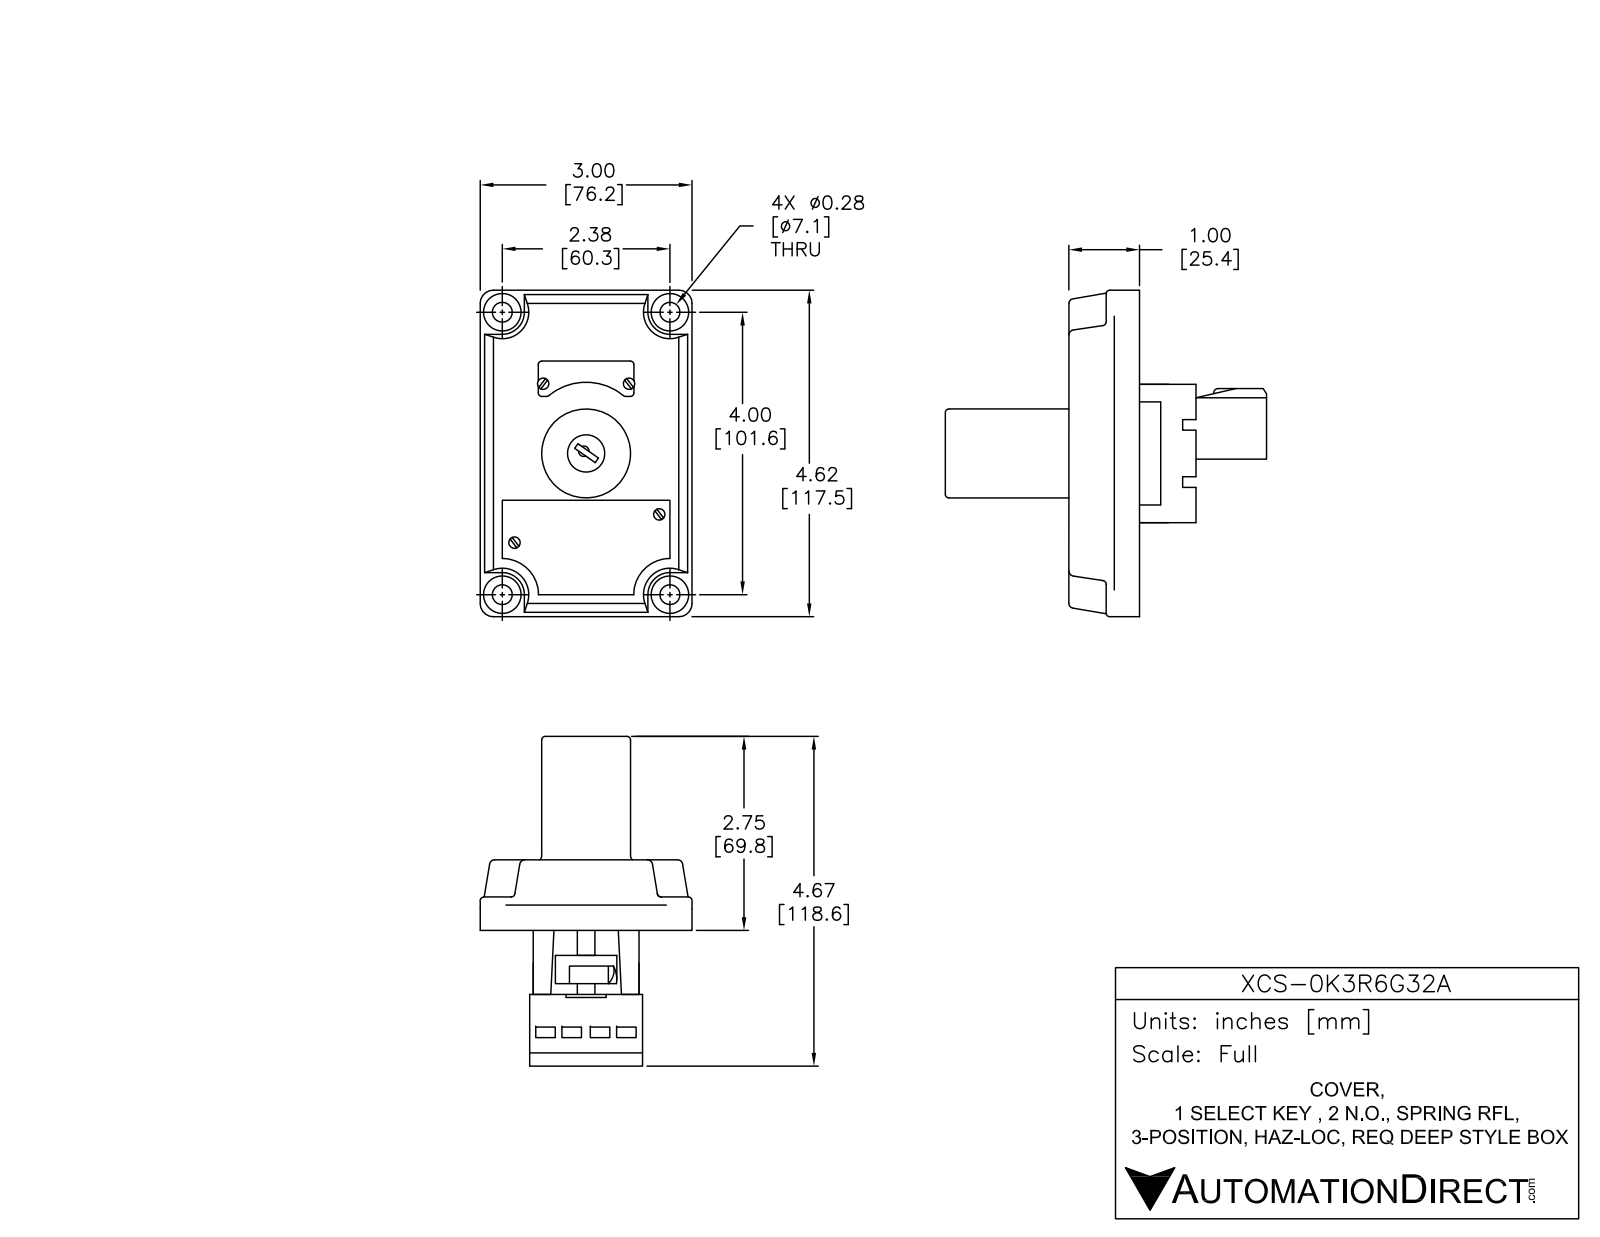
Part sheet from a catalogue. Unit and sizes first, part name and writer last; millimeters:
Units: millimetres
Overall size (bounding box): 117.6 × 106.46 × 78.74
Round holes (diameter × count): ⌀6.65 ×4, ⌀6.86 ×4, ⌀13.41 ×1
Round bosses / shafts (diameter × count): ⌀3.3 ×6, ⌀11.6 ×4, ⌀6.35 ×4, ⌀32 ×1
Partial cylindrical surfaces — rounded edges, fillets, slot ends (radius × count): R0.25 ×28, R1.27 ×10, R0.51 ×8, R1.4 ×8, R3 ×8, R2.38 ×4, R2.54 ×4, R9.65 ×4
Main face-to-face distances: 13.34, 12.7, 26.04, 11.3, 24, 37.34, 17.5, 6.5, 4.8, 30.84
Hole centre spacings: 59.11, 10.2, 20.4, 60.46, 101.6, 118.23, 10.13, 10.18
Volume: 229 688 mm³ · Surface area: 58 343 mm²
Bodies: 10 solids, 476 faces (177 planar, 169 cylindrical, 130 other)
Part name (STEP PRODUCT): XCS-0K3R6G32A
STEP written by: SolidWorks 2015 (AUTOMOTIVE_DESIGN)
